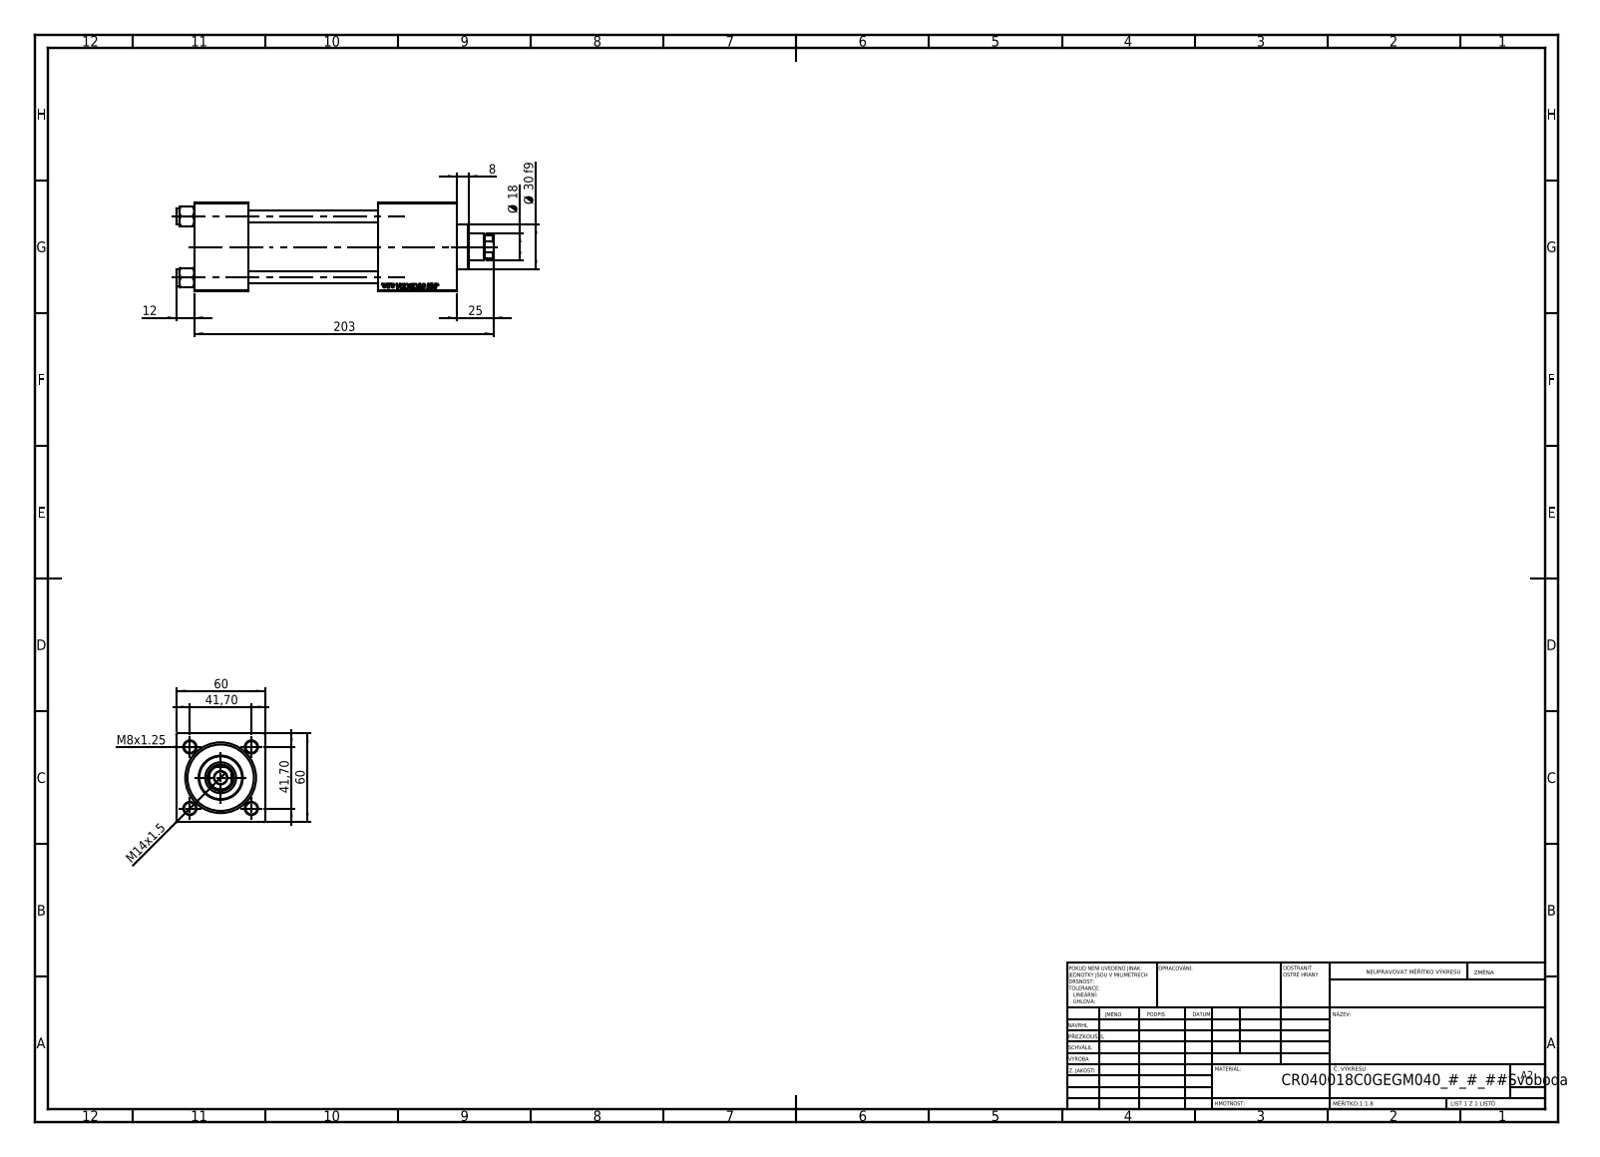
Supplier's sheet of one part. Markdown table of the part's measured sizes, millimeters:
| quantity | value |
| --- | --- |
| part name | NUT_M5_C; V215CR_VCP_C; V215CR_C_Body; V215CR_C_TYCINKA (+1 more) |
| STEP written by | SolidWorks 2019 (CONFIG_CONTROL_DESIGN) |
| units | millimeters |
| bodies | 11 solids, 1149 faces (526 planar, 87 cylindrical, 536 other) |
| overall size | 215 × 60 × 60 |
| volume | 428 314 mm³ |
| surface area | 118 147 mm² |
| round holes (diameter × count) | 8 × 4, 7 × 2, 16.66 × 2, 24 × 2, 8.5 × 1, 18 × 1, 21 × 1, 31 × 1, 40 × 1, 45 × 1 |
| round bosses / shafts (diameter × count) | 11 × 4, 46 × 1, 30 × 1 |
| partial cylindrical surfaces (radius × count) | 8.5 × 1 |
| main face-to-face distances | 60, 37, 178, 141, 53, 125, 88, 149.3, 112.3, 24.3 |
| hole center spacings | 29.49, 41.7, 58.97, 122.5 |
